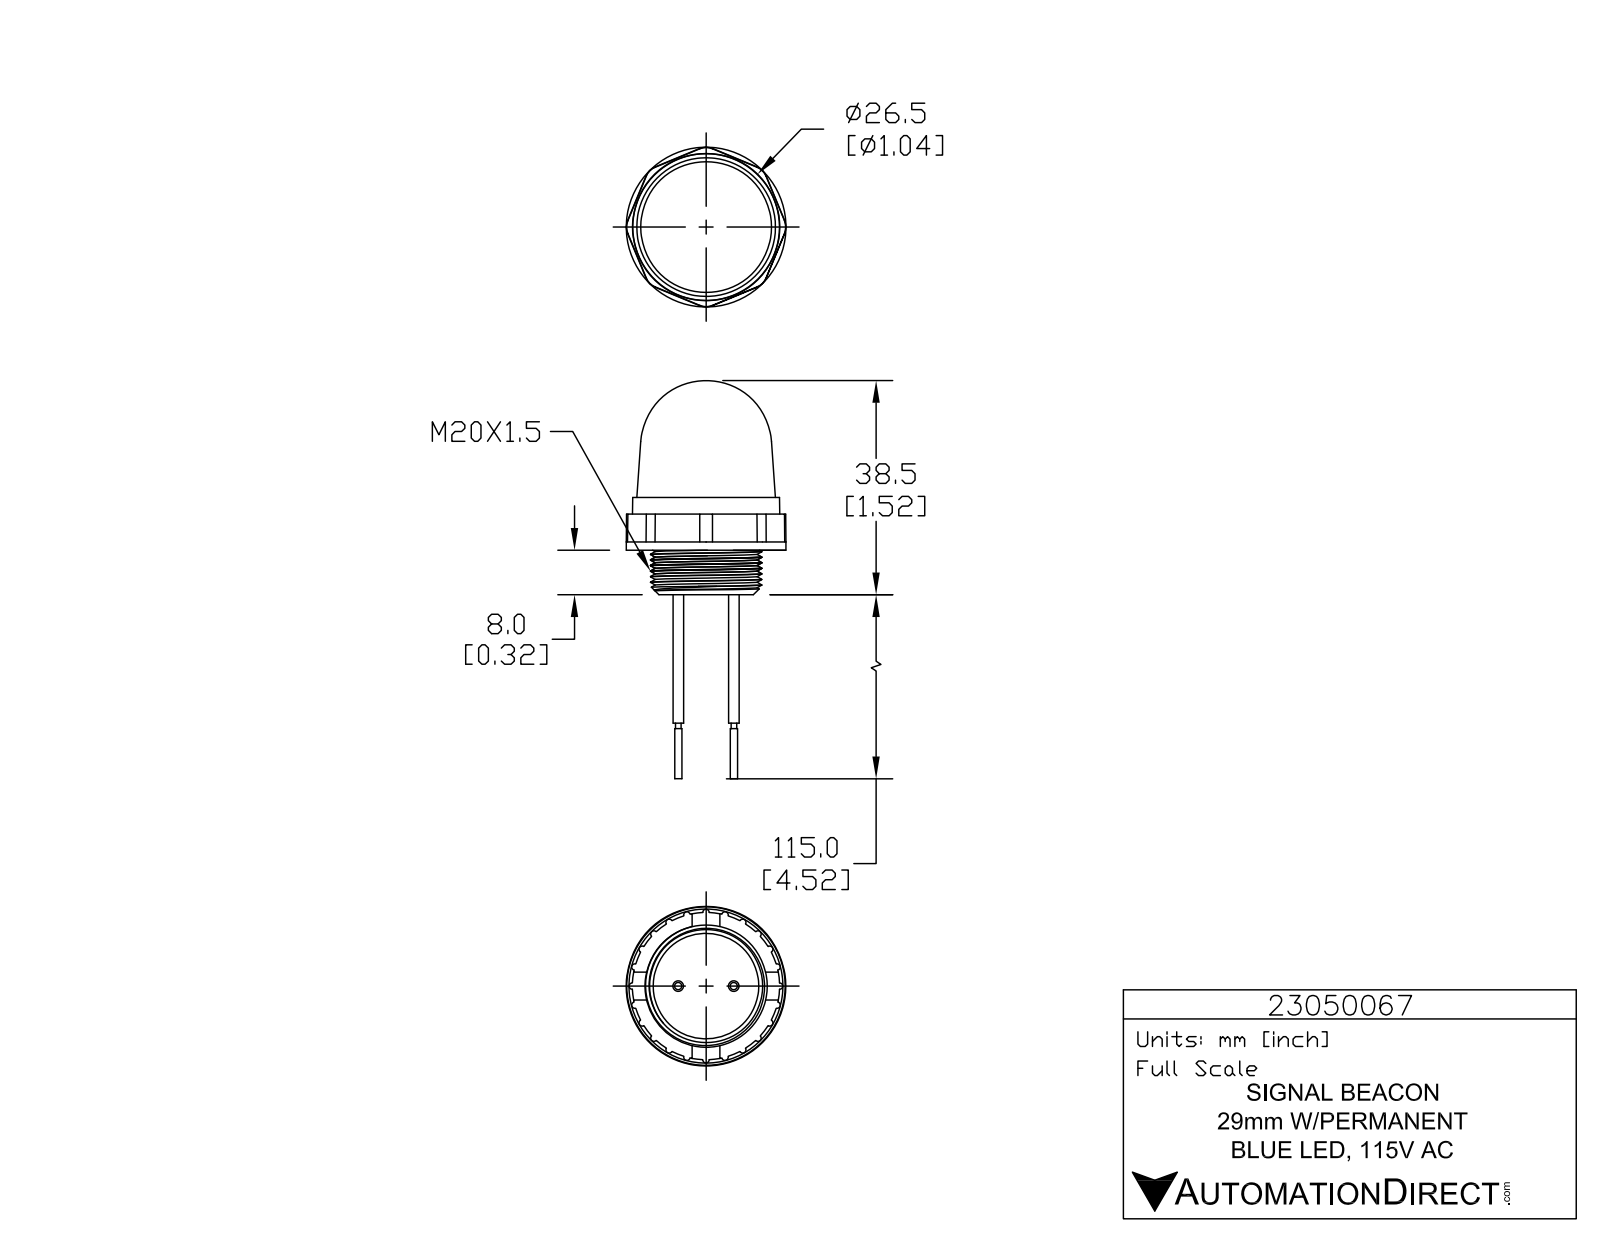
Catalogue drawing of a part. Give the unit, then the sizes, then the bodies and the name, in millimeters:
Units: millimetres
Overall size (bounding box): 71.6 × 28.7 × 28.7
Round holes (diameter × count): ⌀0.5 ×3, ⌀20.5 ×1
Round bosses / shafts (diameter × count): ⌀2.9 ×3, ⌀0.7 ×3, ⌀1.9 ×2, ⌀1.3 ×2, ⌀1 ×2, ⌀28.7 ×1, ⌀28.5 ×1, ⌀22.7 ×1
Partial cylindrical surfaces — rounded edges, fillets, slot ends (radius × count): R3 ×8, R0.1 ×6, R0.1 ×6, R0.1 ×6, R1.7 ×6, R0.1 ×3, R0.2 ×3, R0.2 ×3
Main face-to-face distances: 7, 9.5, 1, 8, 16.5, 16.2, 9.2, 17.5, 10.5, 1.3
Volume: 16 000 mm³ · Surface area: 5 263 mm²
Bodies: 1 solid, 844 faces (551 planar, 203 cylindrical, 90 other)
Part name (STEP PRODUCT): 23050067
STEP written by: SolidWorks 2017 (AUTOMOTIVE_DESIGN)
